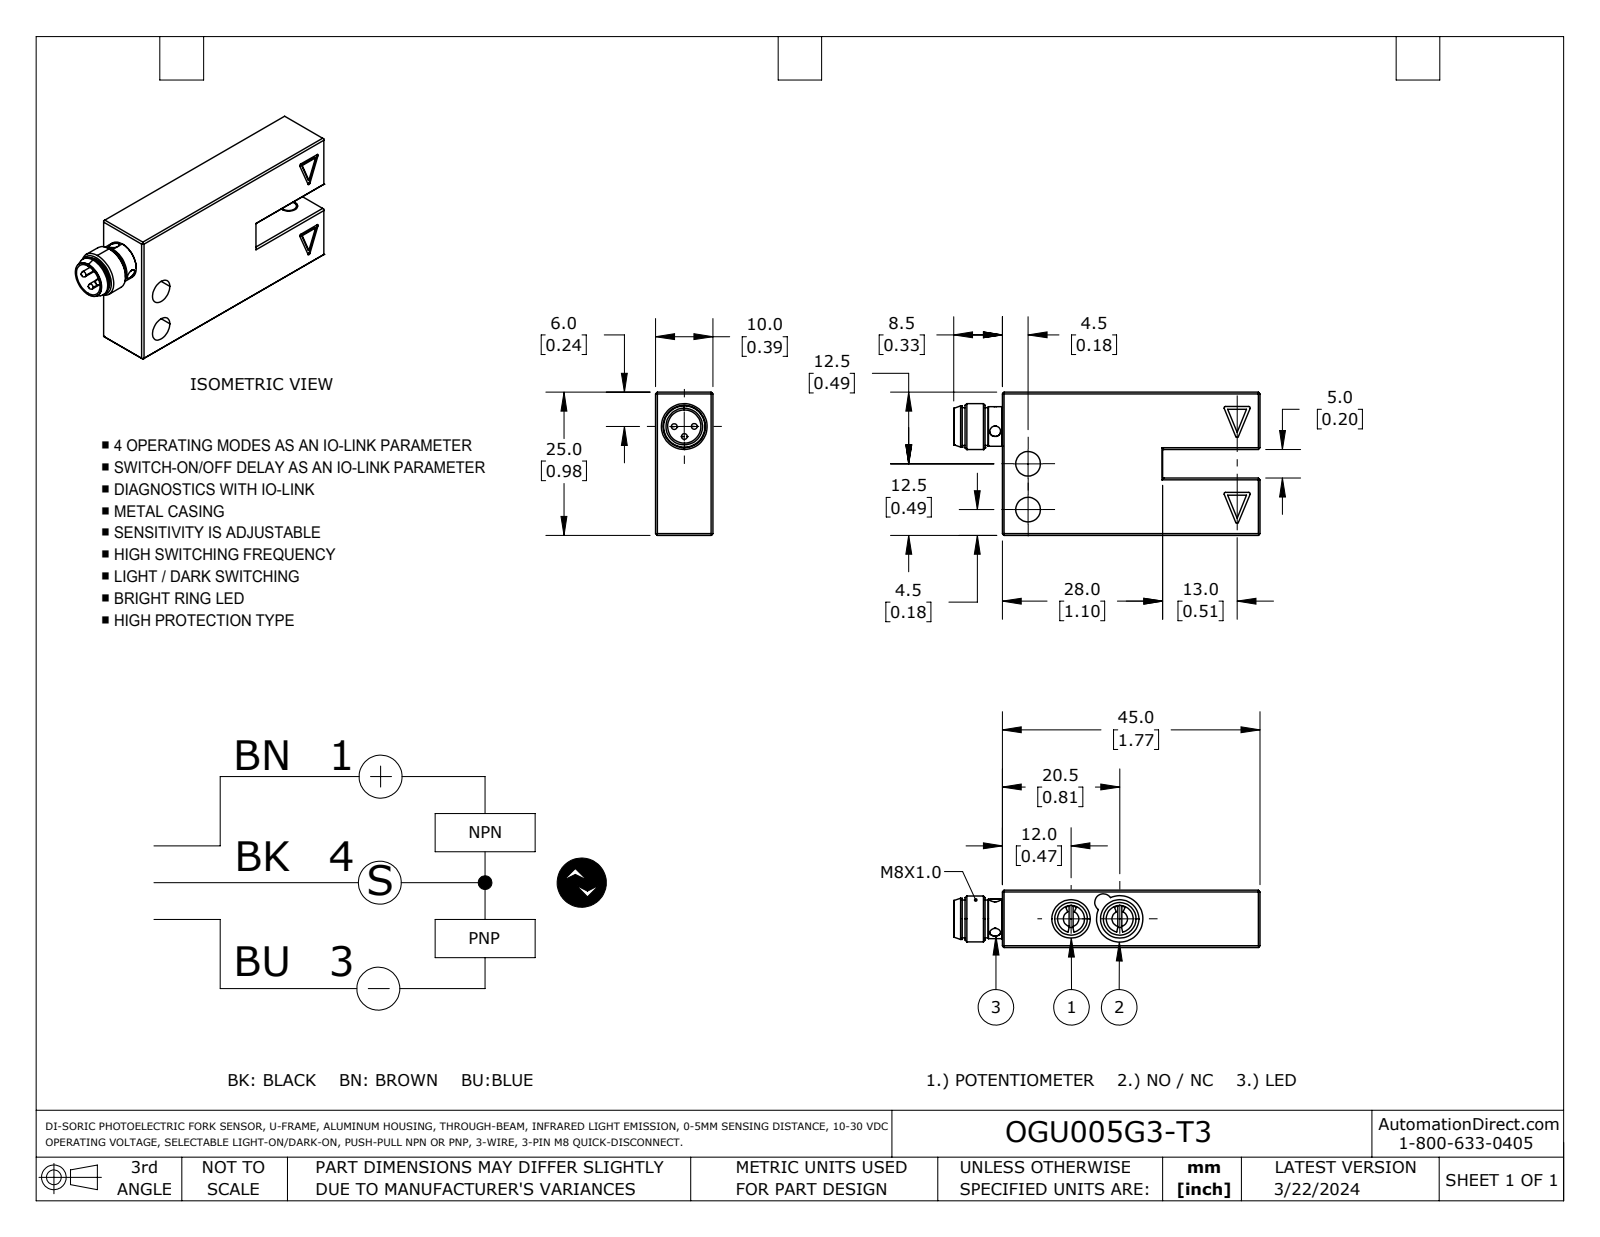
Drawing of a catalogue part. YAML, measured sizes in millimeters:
part_name: "OGU005G3-T3"
step_written_by: "SolidWorks 2023 (AUTOMOTIVE_DESIGN)"
units: millimeters
bodies: {solids: 1, faces: 232, planar: 155, cylindrical: 65, other: 12}
overall_size: [53.5, 25, 10]
volume: 10100
surface_area: 4768
round_holes:
  - {diameter: 1.9, count: 3}
  - {diameter: 4.3, count: 2}
  - {diameter: 4.7, count: 2}
  - {diameter: 6.7, count: 2}
  - {diameter: 2, count: 1}
  - {diameter: 3.1, count: 1}
  - {diameter: 5.8, count: 1}
  - {diameter: 8.1, count: 1}
round_bosses_or_shafts:
  - {diameter: 6.6, count: 3}
  - {diameter: 1, count: 3}
  - {diameter: 8, count: 1}
  - {diameter: 7.2, count: 1}
  - {diameter: 6.9, count: 1}
  - {diameter: 6.4, count: 1}
  - {diameter: 5.7, count: 1}
partial_cylinders:
  - {radius: 0.3, count: 6}
  - {radius: 1.5, count: 6}
  - {radius: 1.3, count: 2}
  - {radius: 2.3, count: 2}
  - {radius: 0.9, count: 1}
face_to_face_distances: [10, 25, 15, 5, 45, 3, 2, 17, 0.5, 28]
hole_center_spacings: [8, 8.5, 20.5, 29]
